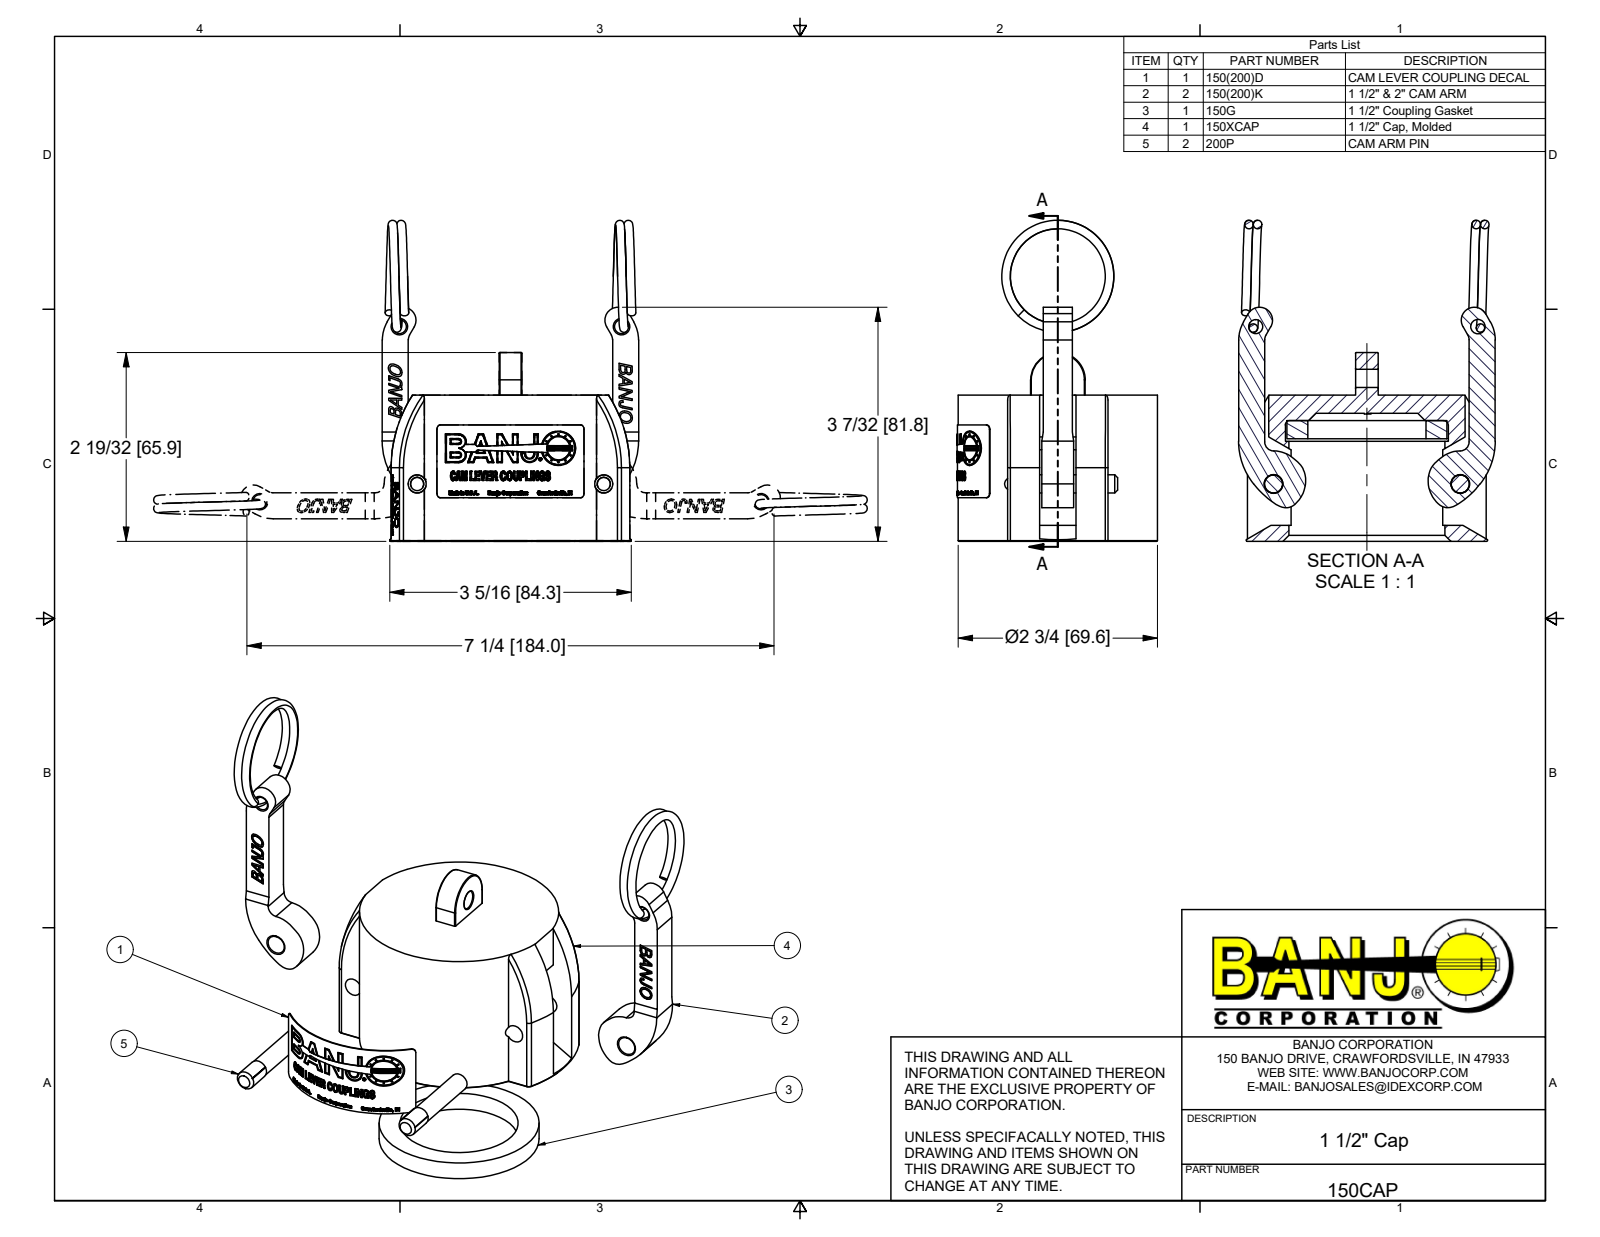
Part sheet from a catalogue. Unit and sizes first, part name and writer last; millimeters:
Units: millimetres
Overall size (bounding box): 112.1 × 89.6 × 70
Round holes (diameter × count): ⌀6.4 ×3, ⌀5 ×2, ⌀6.6 ×2, ⌀8.1 ×1, ⌀11.4 ×1, ⌀41.3 ×1, ⌀54.5 ×1, ⌀56.9 ×1
Round bosses / shafts (diameter × count): ⌀6.6 ×2, ⌀6.3 ×2, ⌀55.9 ×1, ⌀12 ×1
Partial cylindrical surfaces — rounded edges, fillets, slot ends (radius × count): R1.5 ×8, R0.3 ×4, R0.7 ×2, R1 ×2, R2.4 ×2, R2.6 ×2, R3.1 ×2, R3.2 ×2
Main face-to-face distances: 8.9, 6.4, 51.1, 42.2, 15.2, 35.8, 11.2, 23.9, 44.7, 2.5
Hole centre spacings: 55.3, 90.1, 20.1, 47.8, 50.9, 65.2, 70, 77.6
Volume: 129 200 mm³ · Surface area: 50 740 mm²
Bodies: 9 solids, 1947 faces (962 planar, 238 cylindrical, 747 other)
Part name (STEP PRODUCT): 150CAP; 150XCAP; 150(200)D-150; 150(200)K (+4 more)
STEP written by: Autodesk Inventor 2019 (AUTOMOTIVE_DESIGN)
